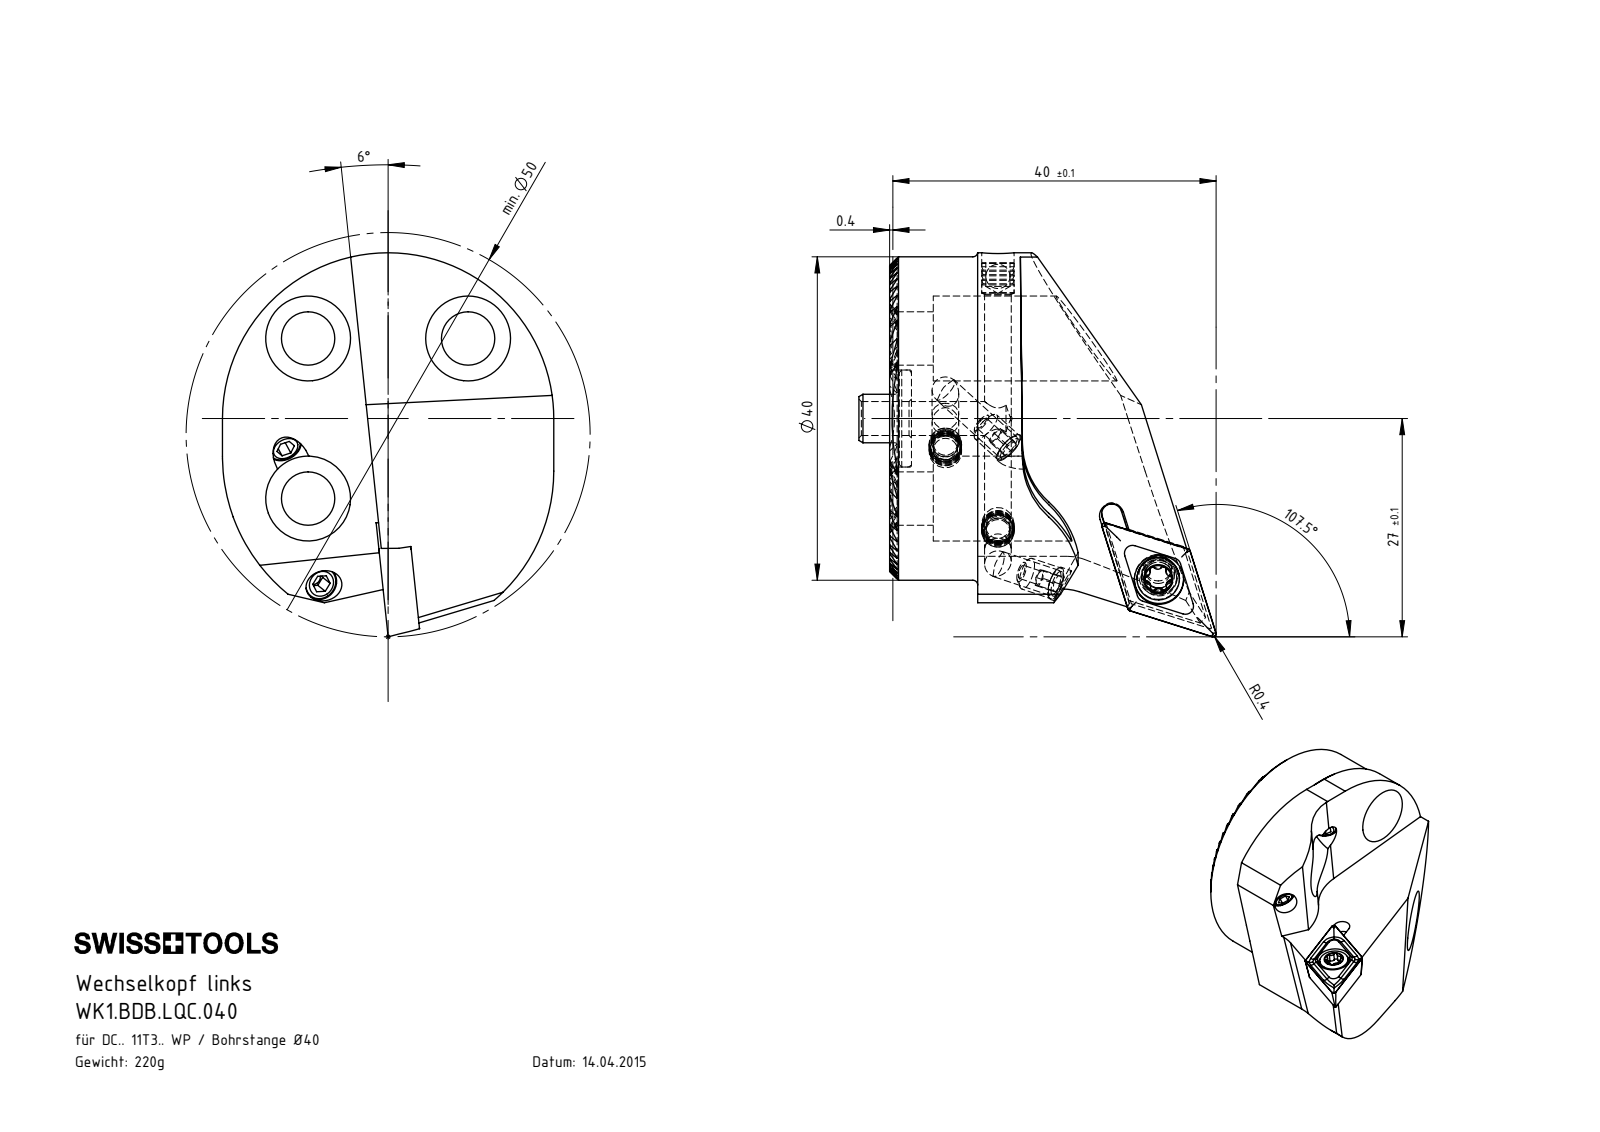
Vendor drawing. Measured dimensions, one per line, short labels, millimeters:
name: WK1.BDB.LQC.040; DCMT11T304; WK1-BDB.LQC.040_A; WKX-ER1.004.005_A_PreviewCfg (+3 more)
written by: SolidWorks 2017 (AUTOMOTIVE_DESIGN)
unit: mm
bodies: 12 solids, 604 faces (219 planar, 207 cylindrical, 178 other)
size: 47.51 × 44.2 × 41
volume: 27 796 mm³; area: 11 820 mm²
holes: 6× ⌀3.3, 3× ⌀3, 3× ⌀4.2, 3× ⌀6.6, 3× ⌀10.5, 2× ⌀1.7, 1× ⌀4, 1× ⌀4.4, 1× ⌀6.1, 1× ⌀12
bosses: 6× ⌀4, 1× ⌀40, 1× ⌀6, 1× ⌀5.25
rounds: 26× R0.12, 6× R0.34, 6× R0.59, 1× R1.25, 1× R7, 1× R10, 1× R12, 1× R20.5
face distances: 1.3, 2.6, 3.9, 12.99, 5.2, 11.69, 9.09, 10.39, 7.79, 6.5
hole spacings: 14, 19.8, 28
